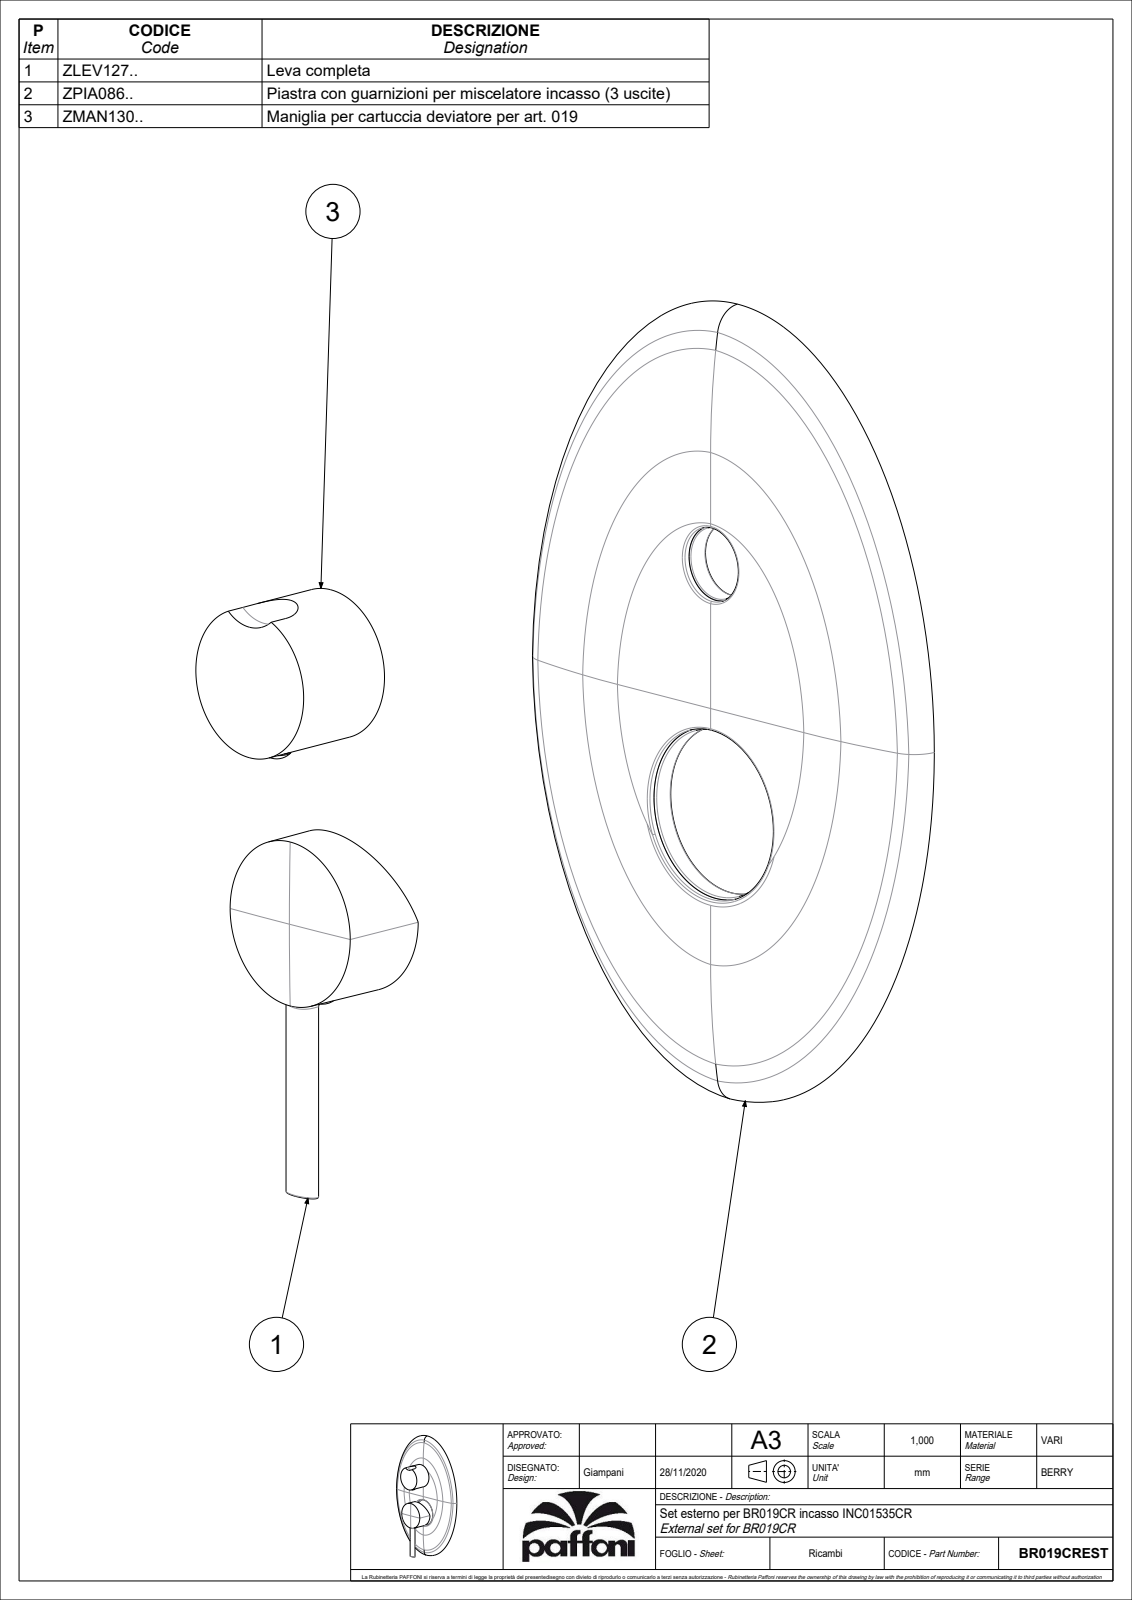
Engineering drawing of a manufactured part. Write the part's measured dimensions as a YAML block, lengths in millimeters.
part_name: "BR019CREST"
step_written_by: "CREO PARAMETRIC BY PTC INC, 2020044 (CONFIG_CONTROL_DESIGN)"
units: millimeters
bodies: {solids: 3, faces: 284, planar: 84, cylindrical: 81, other: 119}
overall_size: [216, 146, 46.68]
volume: 96586
surface_area: 74609
round_holes:
  - {diameter: 3, count: 2}
  - {diameter: 3.2, count: 1}
  - {diameter: 3.5, count: 1}
  - {diameter: 4.2, count: 1}
  - {diameter: 7.8, count: 1}
  - {diameter: 14.8, count: 1}
  - {diameter: 19.2, count: 1}
  - {diameter: 20, count: 1}
  - {diameter: 21, count: 1}
  - {diameter: 23.2, count: 1}
  - {diameter: 36, count: 1}
  - {diameter: 45, count: 1}
round_bosses_or_shafts:
  - {diameter: 7.6, count: 2}
  - {diameter: 5.5, count: 2}
  - {diameter: 51, count: 1}
  - {diameter: 49, count: 1}
  - {diameter: 40, count: 1}
  - {diameter: 25, count: 1}
  - {diameter: 24, count: 1}
  - {diameter: 23, count: 1}
partial_cylinders:
  - {radius: 1.25, count: 4}
  - {radius: 0.8, count: 2}
  - {radius: 1, count: 2}
  - {radius: 1.9, count: 1}
  - {radius: 2.5, count: 1}
  - {radius: 12.5, count: 1}
face_to_face_distances: [39, 9, 2, 14, 30, 37, 28, 16, 23, 18]
hole_center_spacings: [0.5, 6.5, 7, 10, 68, 78]
